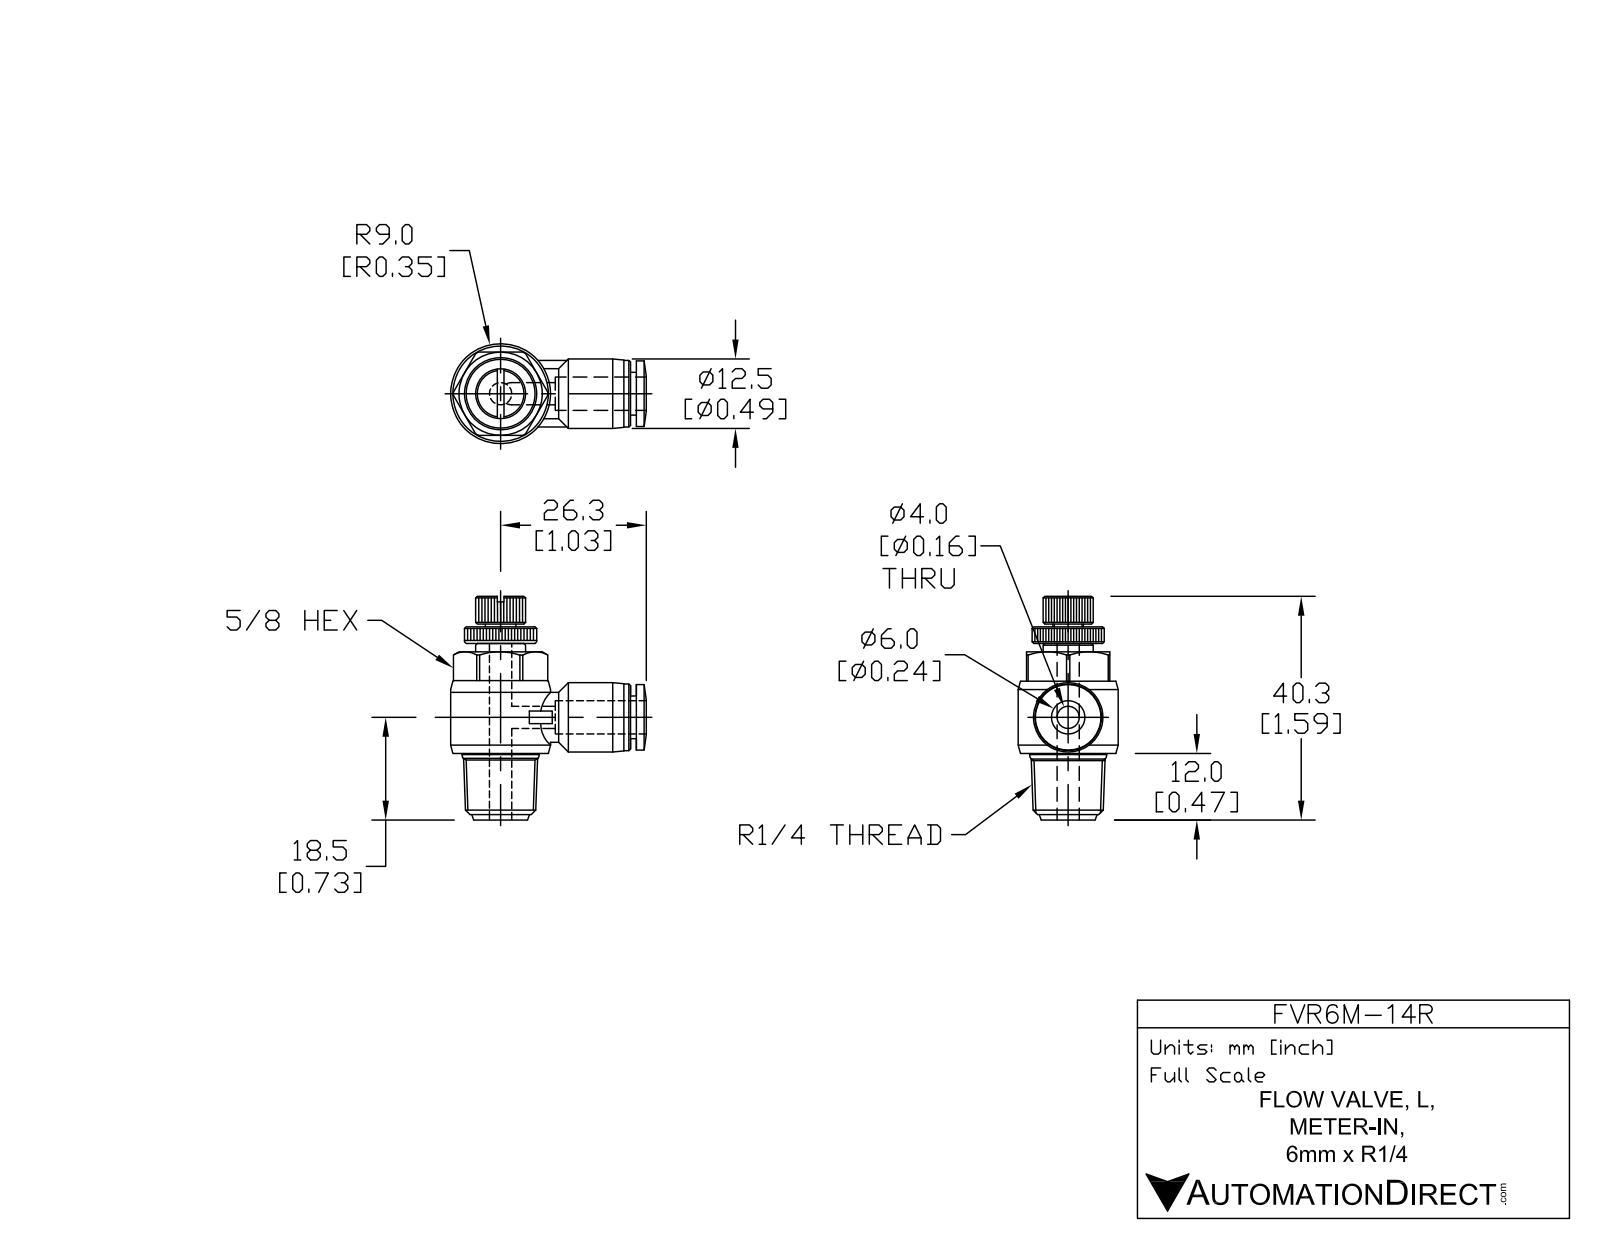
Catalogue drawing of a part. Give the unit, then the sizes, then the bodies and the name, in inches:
Units: inches
Overall size (bounding box): 1.835 × 1.388 × 0.709
Round holes (diameter × count): ⌀0.177 ×2, ⌀0.248 ×1
Round bosses / shafts (diameter × count): ⌀0.354 ×2, ⌀0.709 ×1, ⌀0.528 ×1, ⌀0.492 ×1, ⌀0.472 ×1, ⌀0.465 ×1, ⌀0.303 ×1, ⌀0.217 ×1
Partial cylindrical surfaces — rounded edges, fillets, slot ends (radius × count): R0.256 ×1, R0.335 ×1
Main face-to-face distances: 0.591, 0.177, 0.701, 0.878, 0.059, 1.173, 0.472, 0.76, 0.118, 1.232
Volume: 0.464 in³ · Surface area: 6.407 in²
Bodies: 1 solid, 417 faces (187 planar, 110 cylindrical, 120 other)
Part name (STEP PRODUCT): FVR6M-14R
STEP written by: SolidWorks 2015 (AUTOMOTIVE_DESIGN)
